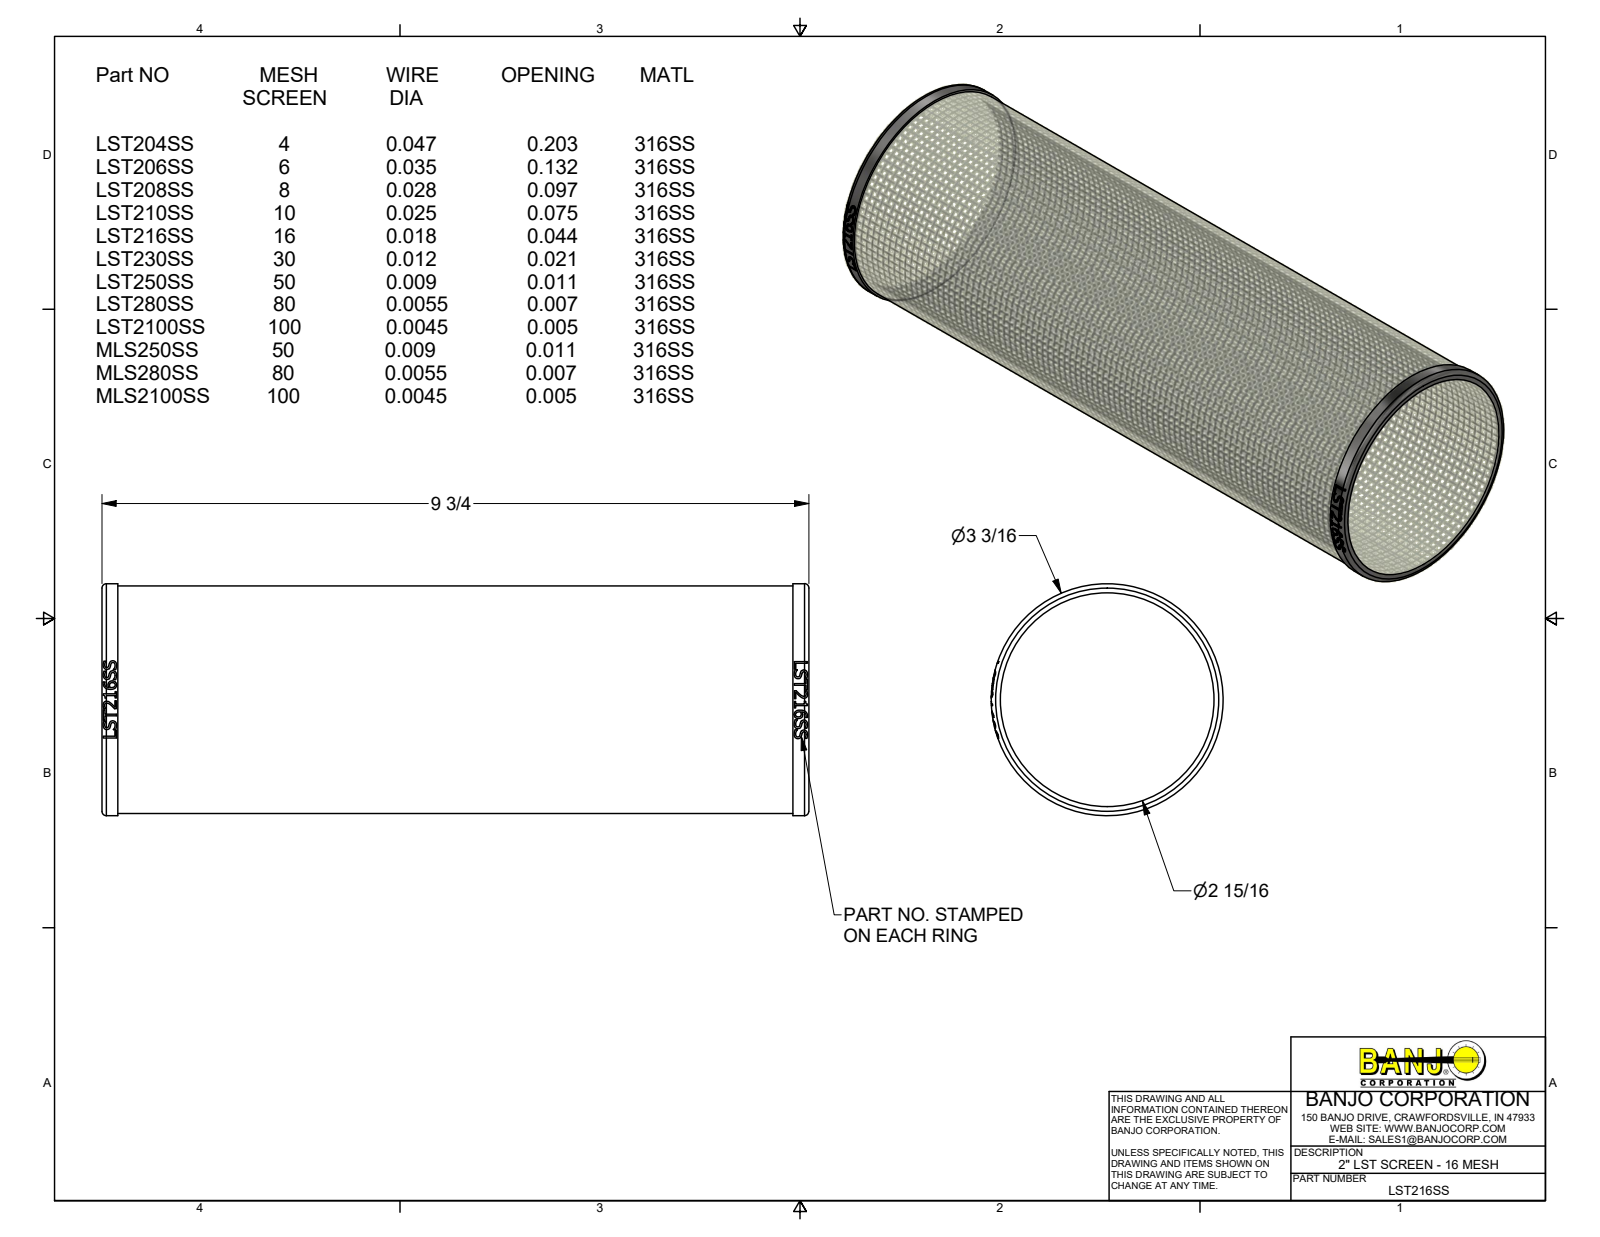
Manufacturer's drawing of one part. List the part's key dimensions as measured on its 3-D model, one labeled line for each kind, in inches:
Part name (STEP PRODUCT): LST216SS
STEP written by: Autodesk Inventor 2019 (AUTOMOTIVE_DESIGN)
Units: inches
Bodies: 1 solid, 274 faces (92 planar, 22 cylindrical, 160 other)
Overall size (bounding box): 9.72 × 3.188 × 3.188
Volume: 8.933 in³ · Surface area: 188 in²
Round holes (diameter × count): ⌀2.937 ×1
Round bosses / shafts (diameter × count): ⌀3.188 ×1, ⌀3.128 ×1
Partial cylindrical surfaces — rounded edges, fillets, slot ends (radius × count): R1.574 ×1
Main face-to-face distances: 9.72, 9.501, 0.219, 9.282, 0.303, 0.444, 0.019, 0.2, 0.02, 9.52
